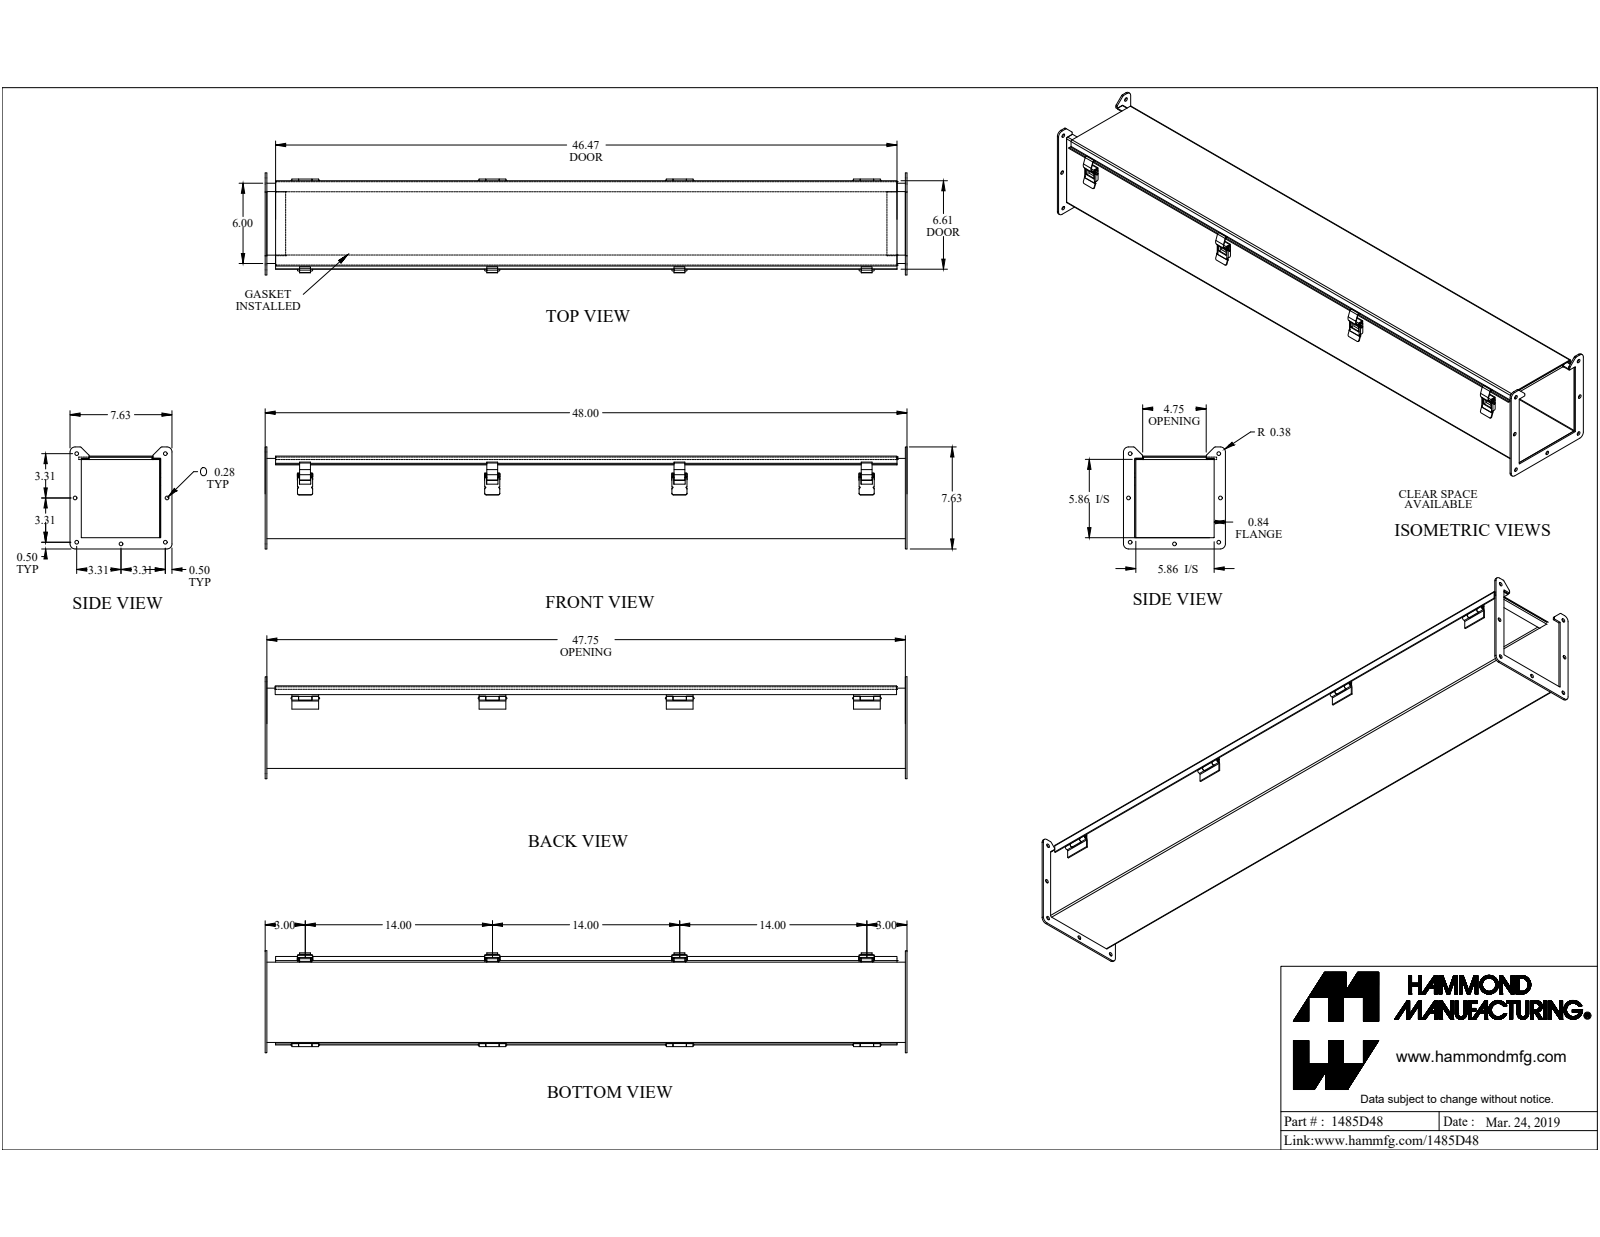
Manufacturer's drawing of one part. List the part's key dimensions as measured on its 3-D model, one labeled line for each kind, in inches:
Part name (STEP PRODUCT): 1485D48
STEP written by: SolidWorks 2019 (CONFIG_CONTROL_DESIGN)
Units: inches
Bodies: 32 solids, 706 faces (418 planar, 280 cylindrical, 8 other)
Overall size (bounding box): 48 × 7.625 × 7.625
Volume: 111.6 in³ · Surface area: 2 889 in²
Round holes (diameter × count): ⌀0.281 ×7, ⌀0.125 ×1, ⌀0.13 ×1, ⌀0.164 ×1
Round bosses / shafts (diameter × count): ⌀0.187 ×2, ⌀0.275 ×1, ⌀0.156 ×1, ⌀0.125 ×1, ⌀0.125 ×1
Partial cylindrical surfaces — rounded edges, fillets, slot ends (radius × count): R0.016 ×25, R0.125 ×13, R0.035 ×9, R0.039 ×9, R0.076 ×9, R0.015 ×8, R0.029 ×8, R0.086 ×8
Main face-to-face distances: 0.072, 5.928, 6.1, 6, 5.856, 6.028, 6.172, 0.172, 5.913, 5.841
Hole centre spacings: 7.519, 6.625, 3.315, 3.315, 9.369, 0.285, 1.112, 1.459
